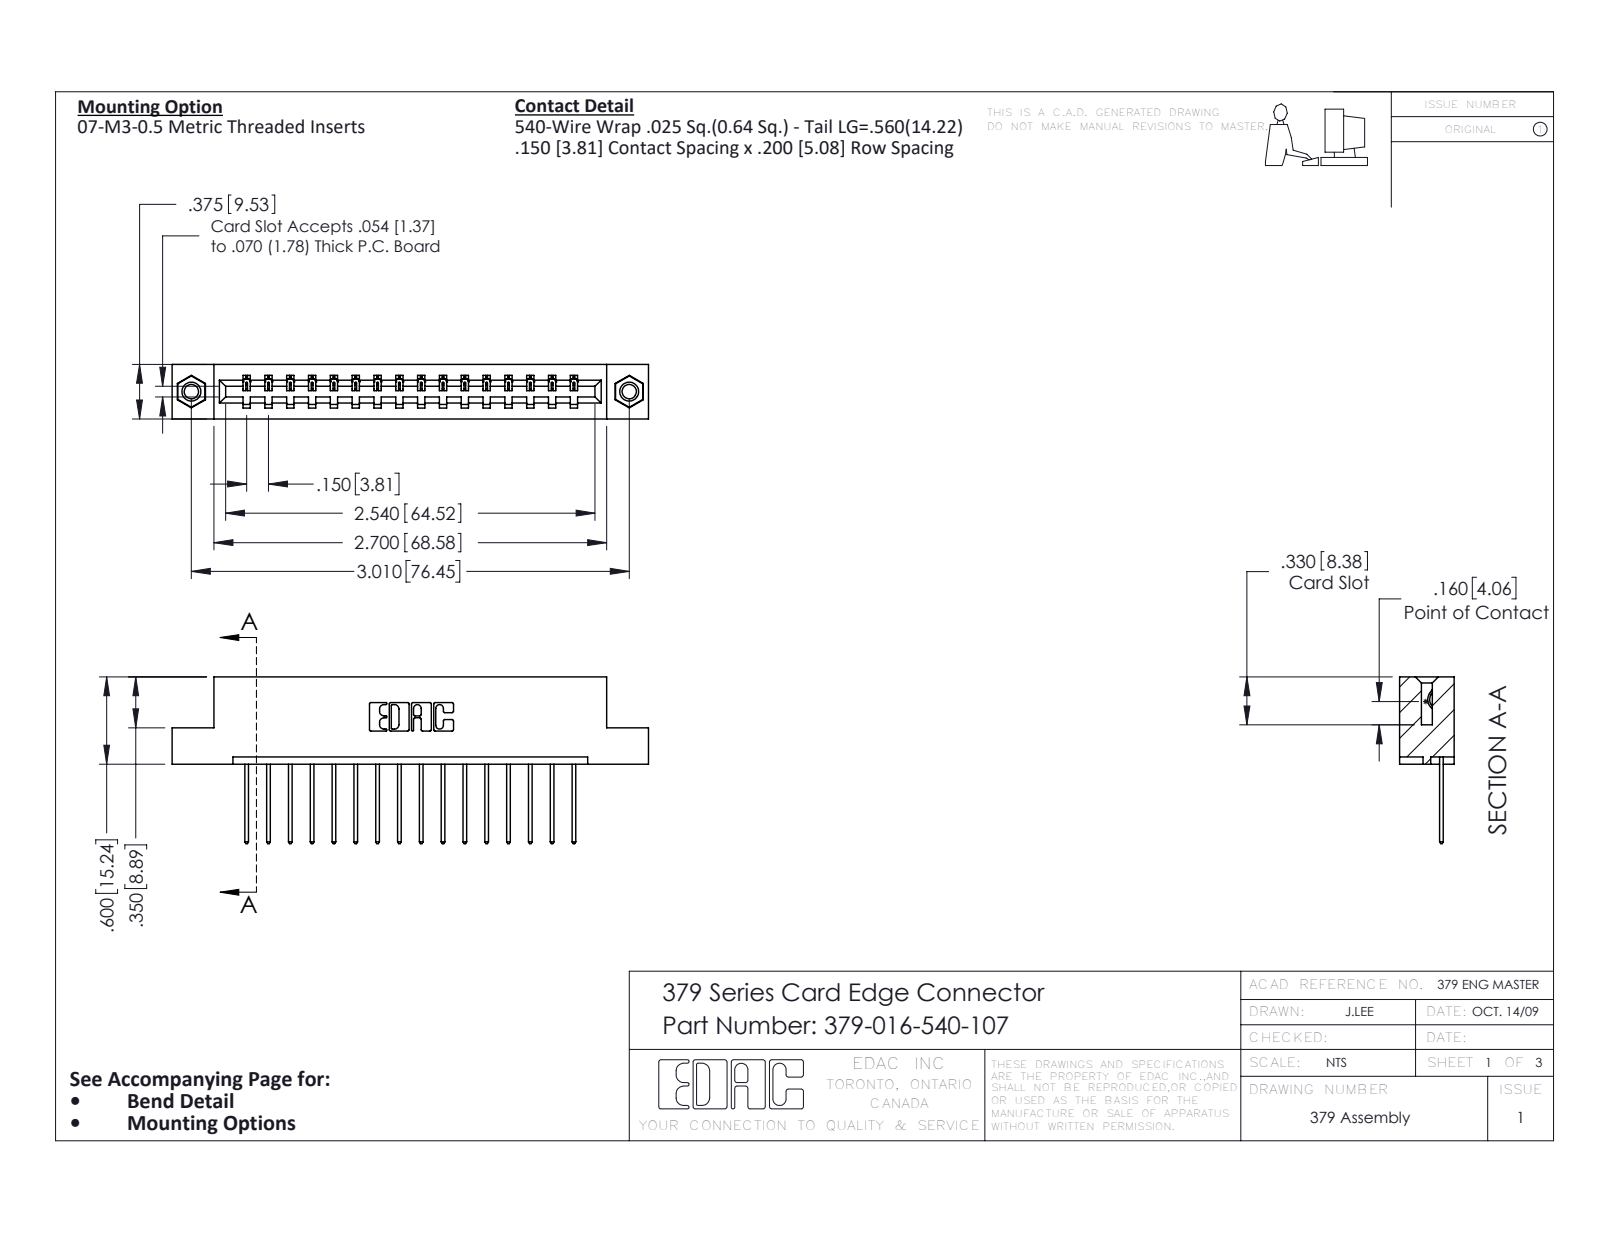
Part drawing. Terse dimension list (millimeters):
name: 379 Part_Flush - .156 Dia - TI; 379-016-540-107; 345-292-001_345-293-140; 345-250-001_345-250-005-103
written by: SolidWorks 2020 (CONFIG_CONTROL_DESIGN)
unit: mm
bodies: 19 solids, 1102 faces (774 planar, 312 cylindrical, 16 other)
size: 83.2 × 29.1 × 9.5
volume: 8 440 mm³; area: 8 703 mm²
holes: 2× ⌀2.5, 2× ⌀3.2, 2× ⌀4
bosses: 2× ⌀3.9
rounds: 32× R0.2, 32× R0.3, 22× R0.3, 6× R0.2, 6× R0.8, 3× R0.7, 1× R0.4, 1× R0.6
face distances: 7.6, 1.9, 9.5, 15.2, 3.8, 5.7, 11.4, 5.1, 19.1, 7
hole spacings: 76.5
